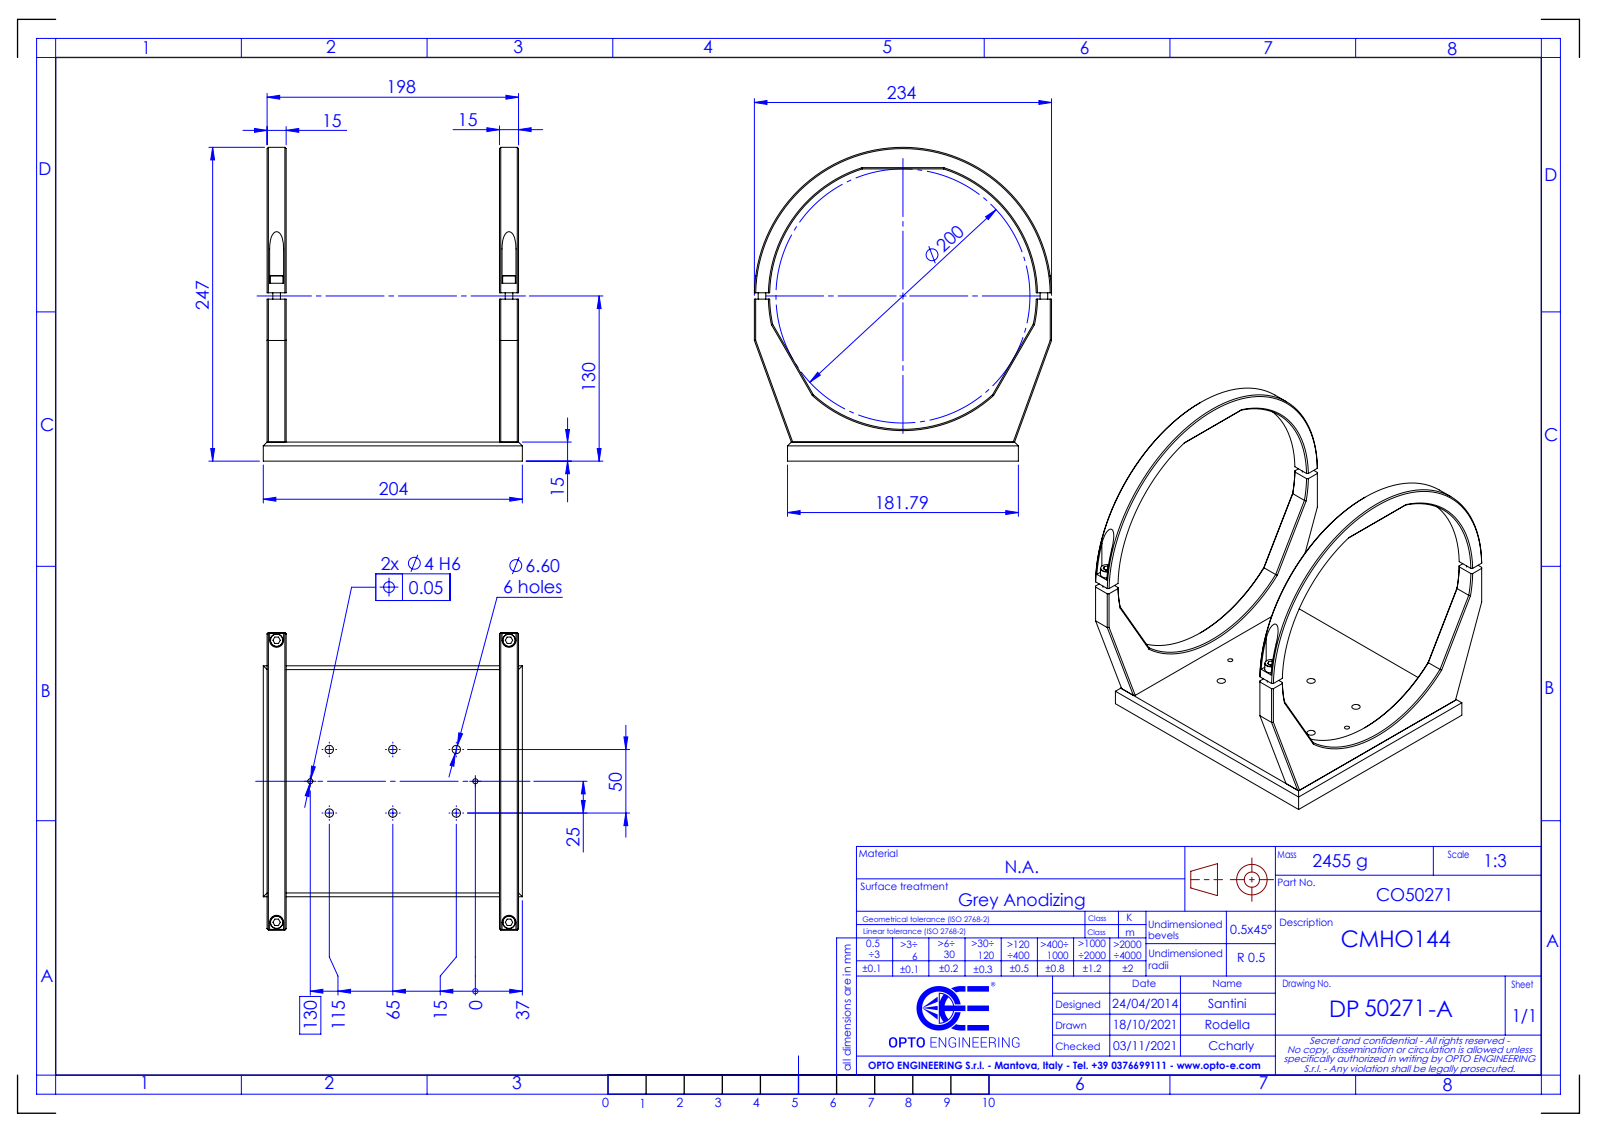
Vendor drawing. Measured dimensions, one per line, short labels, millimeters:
name: DP50271-A_CMHO144
written by: SolidWorks 2021 (CONFIG_CONTROL_DESIGN)
unit: mm
bodies: 0 solids, 236 faces (124 planar, 56 cylindrical, 56 other)
size: 247 × 234 × 204
holes: 6× ⌀6.6, 4× ⌀11, 2× ⌀4
bosses: 4× ⌀10, 4× ⌀6
rounds: 4× R5.5, 1× R105, 1× R117
face distances: 15, 183, 168, 198, 181.78, 3, 18, 186, 201, 204.01
hole spacings: 50, 29.15, 69.64, 70.71, 117.69, 130, 57.63, 57.65
